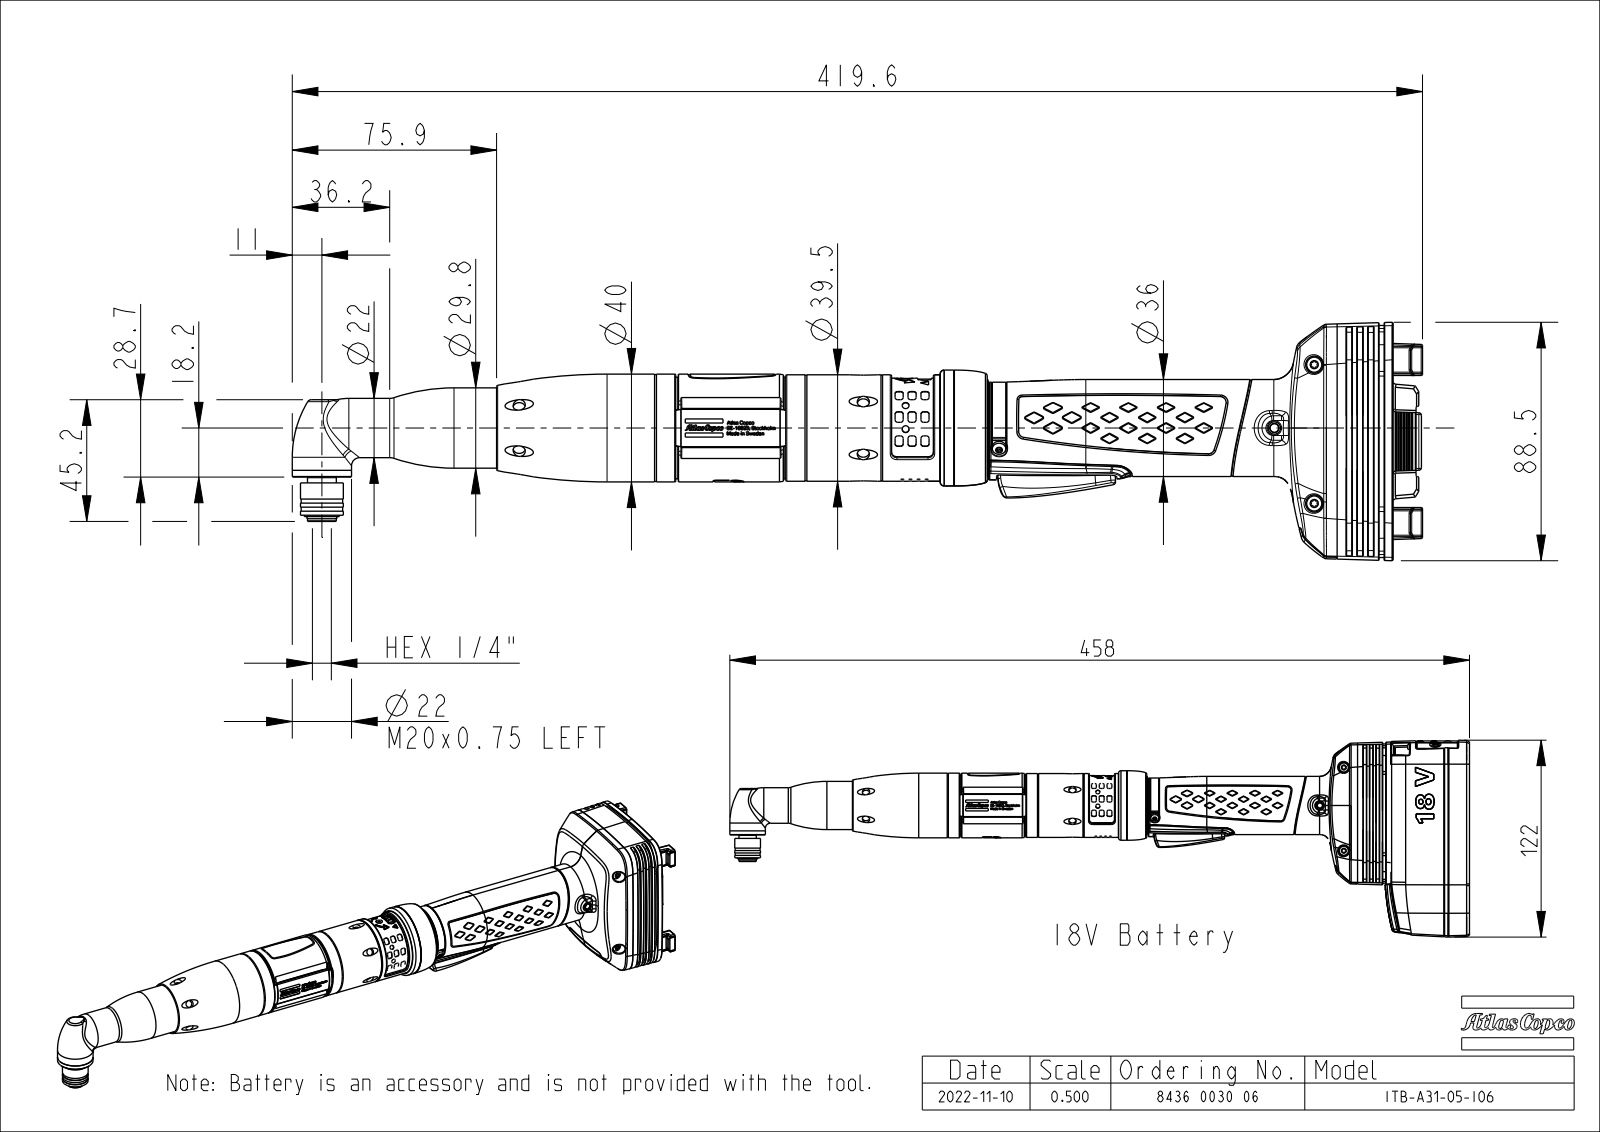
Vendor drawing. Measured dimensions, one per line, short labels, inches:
name: EXT_COMP_SW0004
written by: CREO PARAMETRIC BY PTC INC, 2020281 (CONFIG_CONTROL_DESIGN)
unit: in
bodies: 1 solid, 4846 faces (1488 planar, 993 cylindrical, 2365 other)
size: 16.539 × 3.484 × 2.935
volume: 36.82 in³; area: 132.3 in²
holes: 12× ⌀0.039, 6× ⌀0.177, 4× ⌀0.102, 4× ⌀0.256, 2× ⌀0.063, 2× ⌀0.197, 2× ⌀0.472, 1× ⌀0.126, 1× ⌀0.128, 1× ⌀0.138, 1× ⌀0.186, 1× ⌀0.291
bosses: 4× ⌀0.244, 2× ⌀0.866, 2× ⌀0.22, 1× ⌀1.693, 1× ⌀1.575, 1× ⌀1.555, 1× ⌀1.417, 1× ⌀1.173
rounds: 102× R0.02, 56× R0.039, 37× R0.012, 28× R0.008, 26× R0.079, 18× R0.009, 18× R0.016, 12× R0.011
face distances: 0.079, 0.157, 0.236, 0.315, 0.413, 0.039, 0.394, 0.622, 0.543, 0.266
hole spacings: 0.118, 0.236, 0.346, 0.49, 0.354, 5.049, 0.693, 1.303
